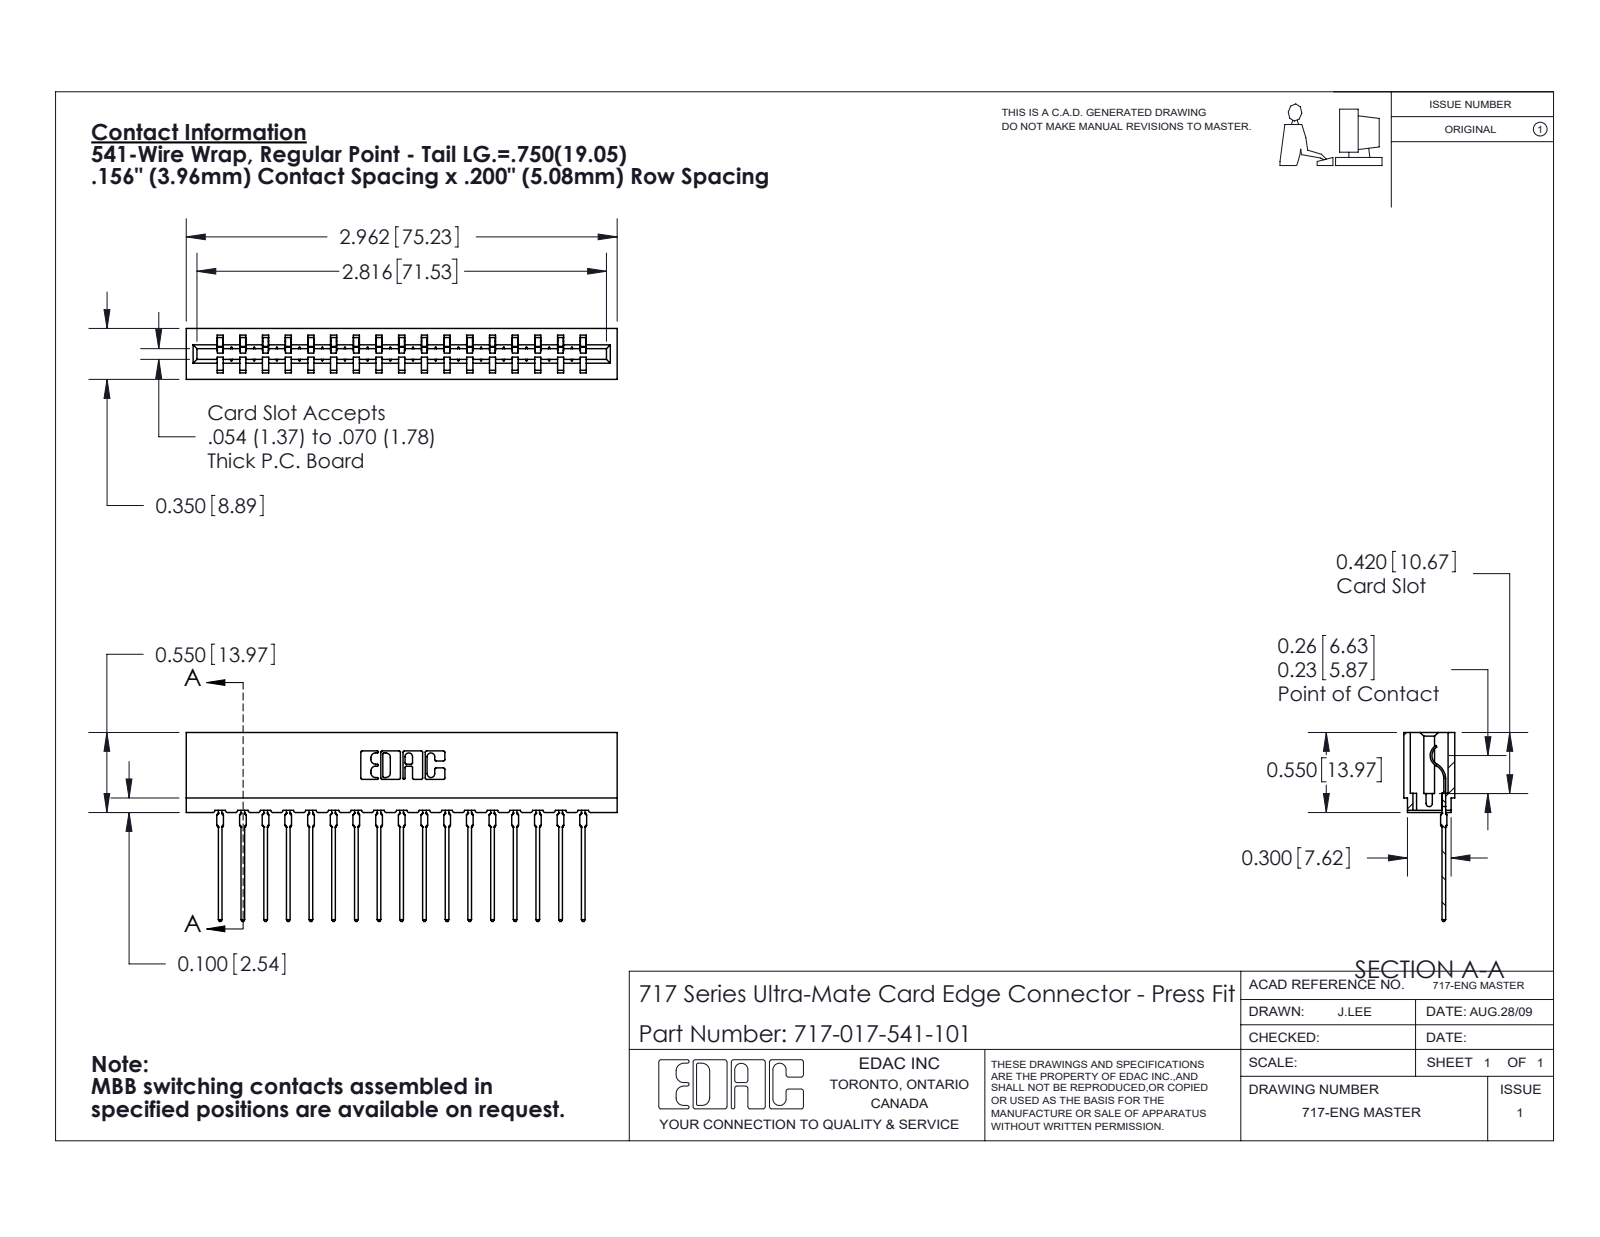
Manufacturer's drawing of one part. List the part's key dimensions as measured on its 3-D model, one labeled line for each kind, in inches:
Part name (STEP PRODUCT): 745-292-001_541; 717-017-541-101; 717 Part_Insulator Option - 06
STEP written by: SolidWorks 2020 (CONFIG_CONTROL_DESIGN)
Units: inches
Bodies: 18 solids, 2015 faces (1210 planar, 363 cylindrical, 442 other)
Overall size (bounding box): 2.962 × 1.299 × 0.35
Volume: 0.399 in³ · Surface area: 14.37 in²
Partial cylindrical surfaces — rounded edges, fillets, slot ends (radius × count): R0.015 ×34, R0.021 ×34, R0.01 ×22, R0.007 ×6, R0.031 ×6, R0.005 ×4, R0.011 ×4, R0.026 ×3
Main face-to-face distances: 0.212, 0.138, 0.35, 0.156, 0.624, 0.468, 0.074, 0.063, 0.287, 0.076
